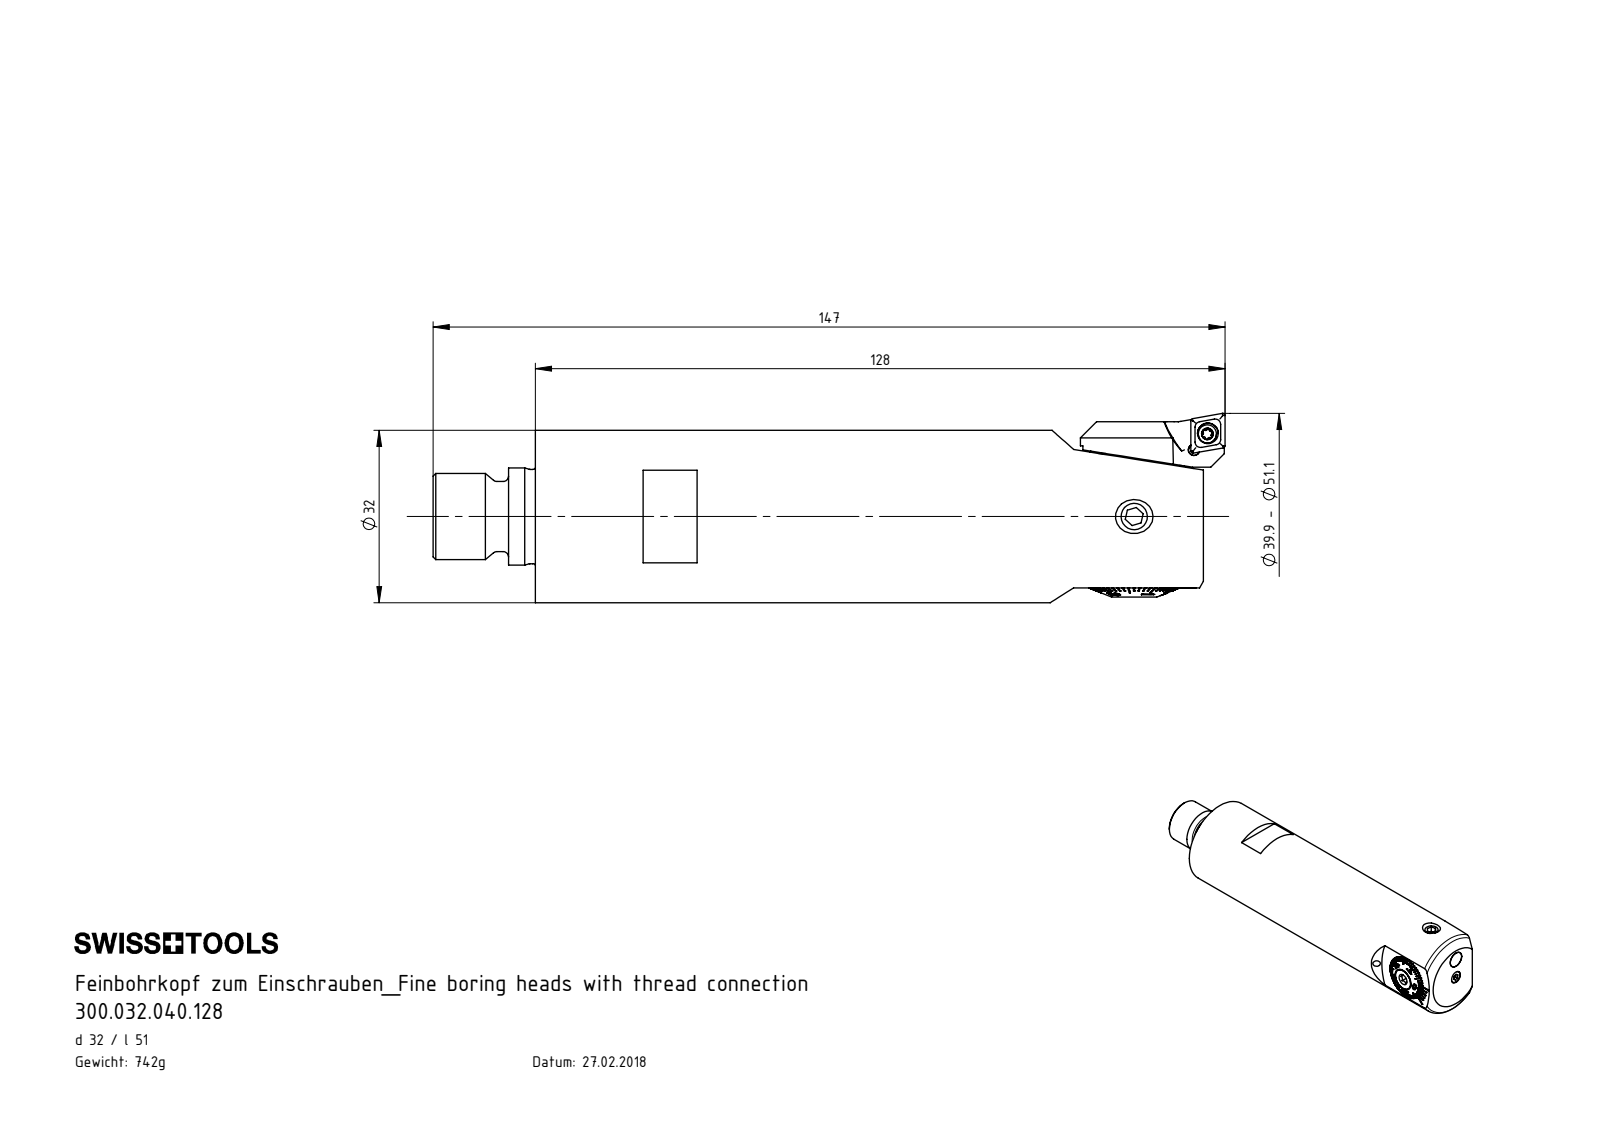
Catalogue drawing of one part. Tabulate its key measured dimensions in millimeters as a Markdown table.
| quantity | value |
| --- | --- |
| part name | F32; F32-BG2.014.012_A; ISO 4026 - M6 x 5; DIN 3771 - 15x1 (+8 more) |
| STEP written by | SolidWorks 2017 (CONFIG_CONTROL_DESIGN) |
| units | millimeters |
| bodies | 12 solids, 628 faces (284 planar, 103 cylindrical, 241 other) |
| overall size | 143 × 32 × 32 |
| volume | 94 796 mm³ |
| surface area | 24 721 mm² |
| round holes (diameter × count) | 2.5 × 4, 5 × 2, 2 × 1, 2.7 × 1, 2.9 × 1, 3 × 1, 6 × 1, 6.8 × 1, 7 × 1, 7.4 × 1, 8.5 × 1, 10.3 × 1 |
| round bosses / shafts (diameter × count) | 32 × 1, 18 × 1, 17.5 × 1, 17 × 1, 16.98 × 1, 16.85 × 1, 16 × 1, 14.65 × 1 |
| partial cylindrical surfaces (radius × count) | 0.5 × 2, 1.75 × 2, 1 × 1, 1.9 × 1, 3.2 × 1 |
| main face-to-face distances | 124, 0.8, 3.7, 4.5, 1.5, 27, 2.2, 2.3, 25.35, 20.85 |
| hole center spacings | 5.7, 8, 11.68 |
